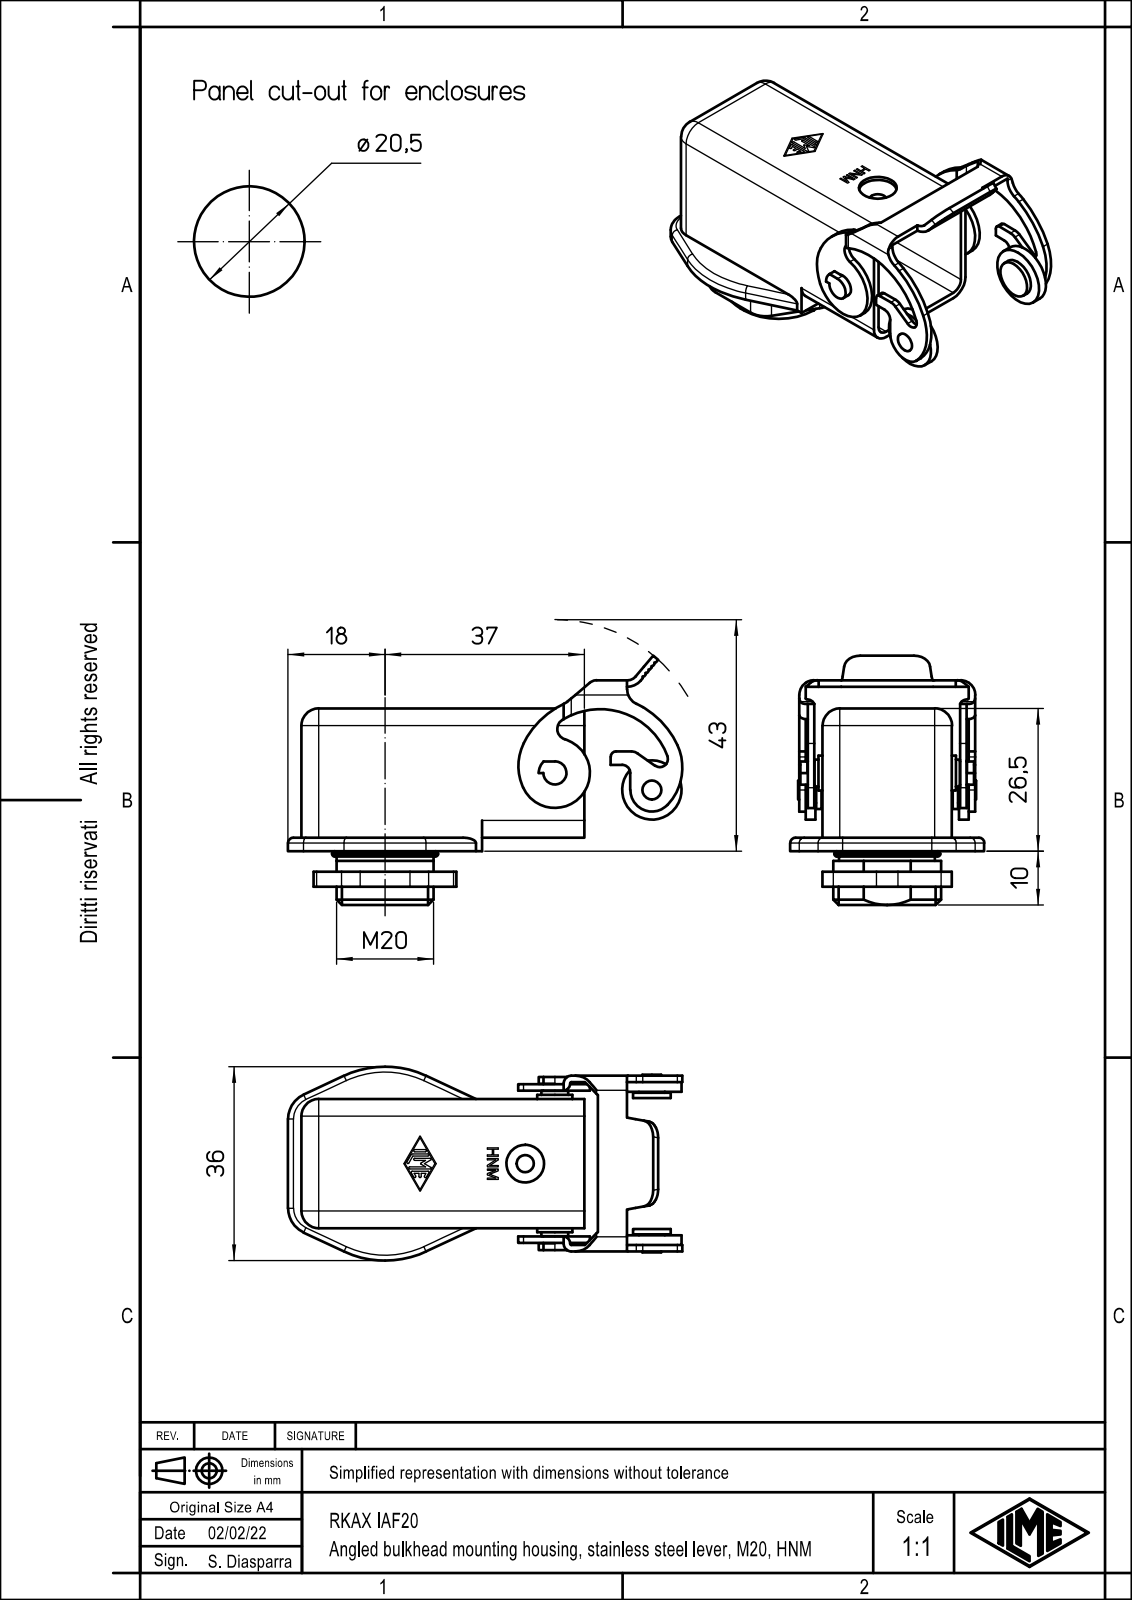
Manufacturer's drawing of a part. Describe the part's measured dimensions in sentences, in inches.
The part is named "RKAX_IAF20". Its 3-D file was written by "Creo Elements/Direct Modeling 20.1B 02-Apr-2019 (C) Parametric Technology GmbH (AUTOMOTIVE_DESIGN)". It is 1 solid with 297 faces: 151 planar, 128 cylindrical and 18 other. Overall it measures 2.88 by 1.823 by 1.417 inches. Its volume is 0.768 cubic inches and its surface area 23.69 square inches. Round holes: 1 of diameter 0.126, 1 of diameter 0.276, 1 of diameter 0.551. Round bosses or shafts: 1 of diameter 0.776, 1 of diameter 0.701, 1 of diameter 0.433, 1 of diameter 0.276, 1 of diameter 0.256, 1 of diameter 0.197, 1 of diameter 0.189, 1 of diameter 0.169. Partial cylindrical surfaces (rounded edges, fillets, slot ends): 13 of radius 0.008, 8 of radius 0.079, 8 of radius 0.126, 7 of radius 0.157, 5 of radius 0.118, 4 of radius 0.055, 3 of radius 0.004, 2 of radius 0.006. The main face-to-face distances are 0.047, 0.898, 0.945, 0.85, 1.043, 0.146, 0.098, 0.996, 0.059, 1.102. The hole center spacings are 1.024.
